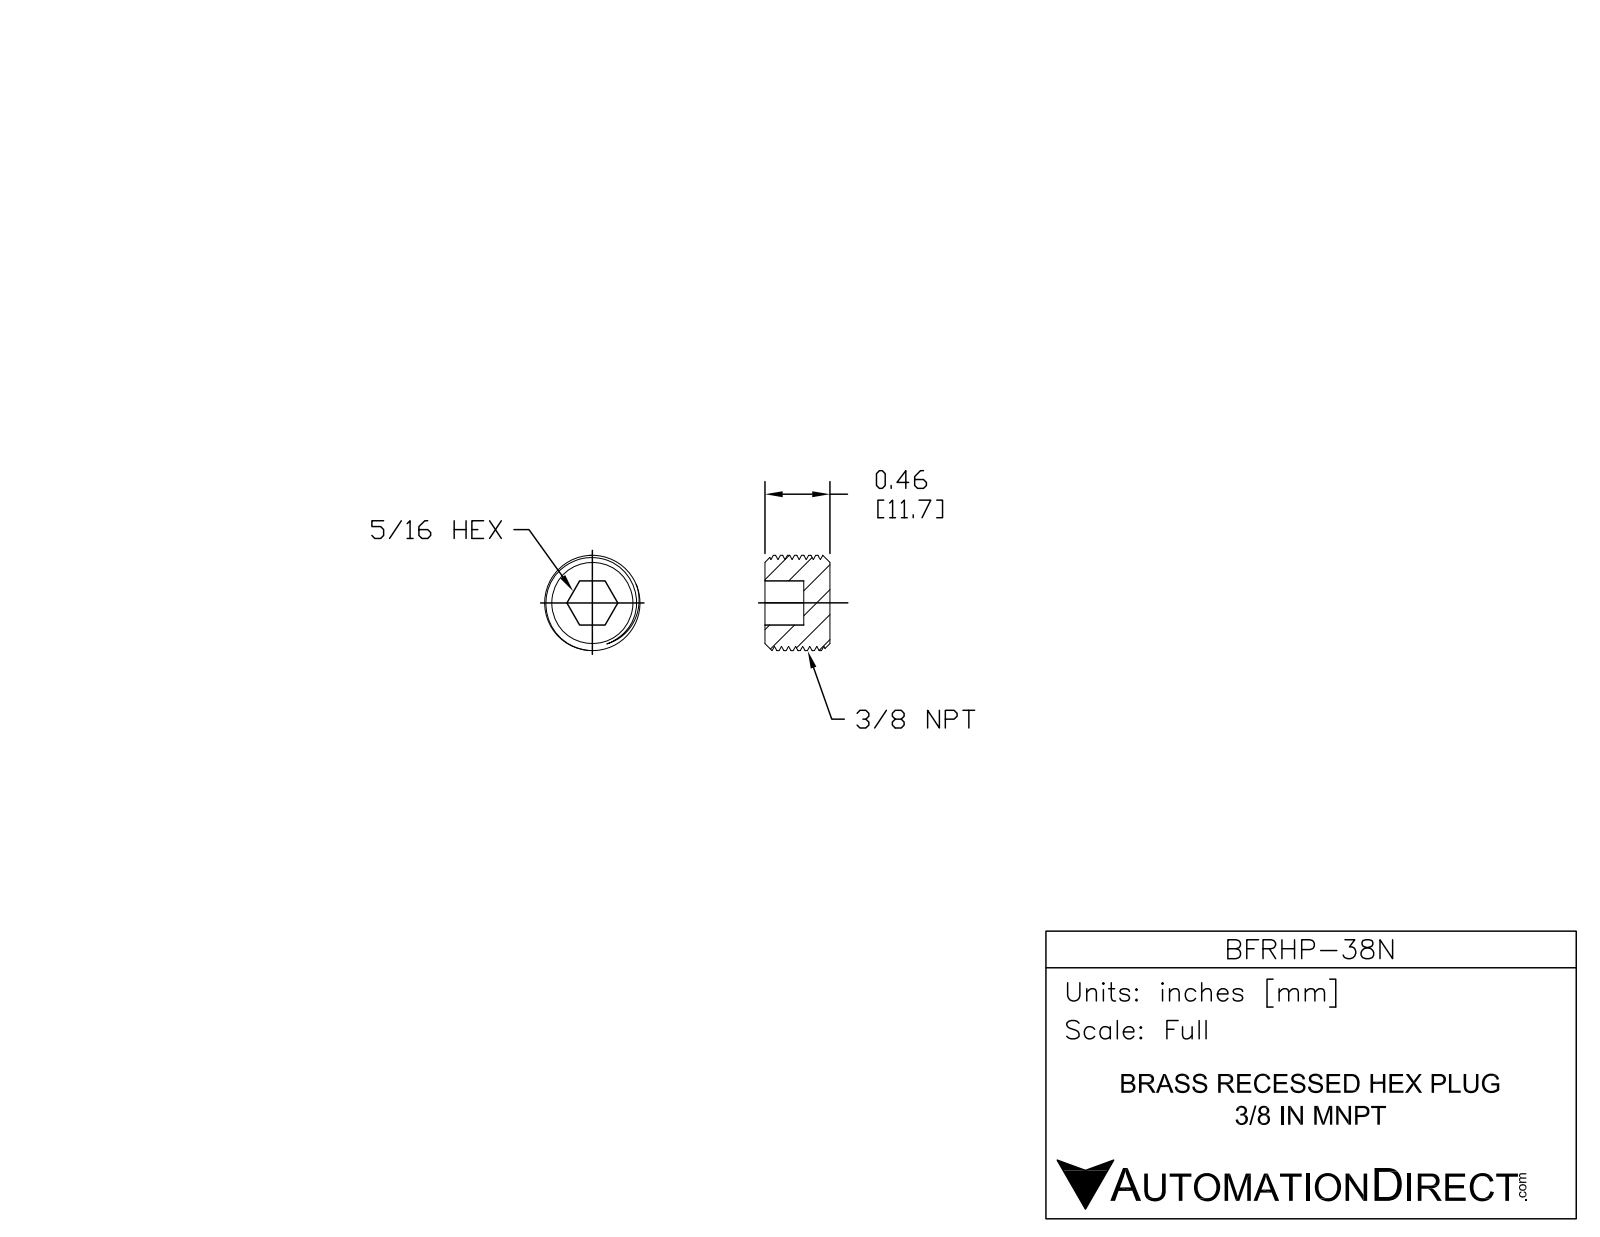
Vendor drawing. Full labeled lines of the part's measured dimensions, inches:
Part name (STEP PRODUCT): BFRHP-38
STEP written by: SolidWorks 2015 (CONFIG_CONTROL_DESIGN)
Units: inches
Bodies: 1 solid, 31 faces (9 planar, 16 cylindrical, 6 other)
Overall size (bounding box): 0.675 × 0.675 × 0.46
Volume: 0.129 in³ · Surface area: 2.351 in²
Round bosses / shafts (diameter × count): ⌀0.675 ×1
Main face-to-face distances: 0.46, 0.185, 0.275
